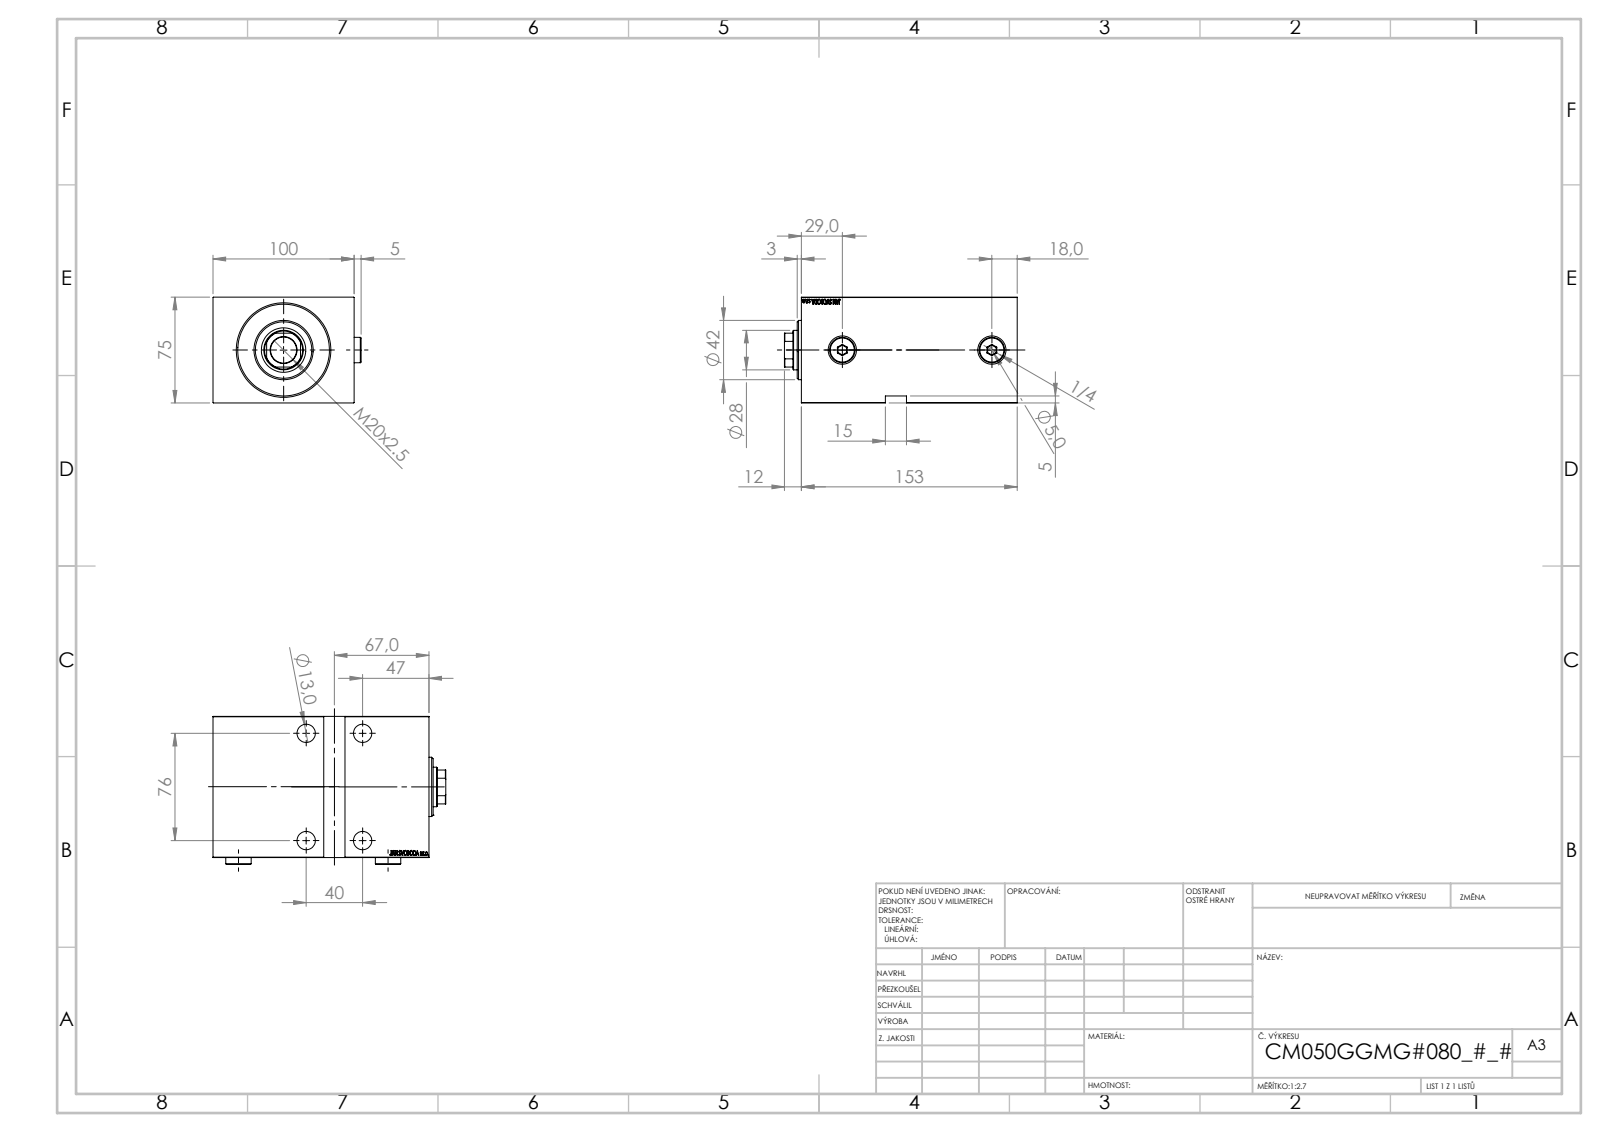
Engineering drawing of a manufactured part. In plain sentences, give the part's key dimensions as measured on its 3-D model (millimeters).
The part is named "V450CM_G_VCP; Zatka_OIL_PORT; V450CM_VC_G; V450CM_G_Body". Its 3-D file was written by "SolidWorks 2019 (CONFIG_CONTROL_DESIGN)". It is 5 solids with 896 faces: 442 planar, 56 cylindrical and 398 other. Overall it measures 165 by 104.9 by 75 millimeters. Its volume is 968 604 cubic millimeters and its surface area 136 611 square millimeters. Round holes: 4 of diameter 13, 4 of diameter 19, 2 of diameter 5, 2 of diameter 13.16, 2 of diameter 20, 1 of diameter 18.5, 1 of diameter 28, 1 of diameter 31.5, 1 of diameter 50, 1 of diameter 52, 1 of diameter 65. Round bosses or shafts: 2 of diameter 18, 1 of diameter 42. Partial cylindrical surfaces (rounded edges, fillets, slot ends): 1 of radius 13.5. The main face-to-face distances are 75, 100, 153, 5, 14, 139, 148, 134, 87, 70. The hole center spacings are 40, 76, 85.88, 106.
